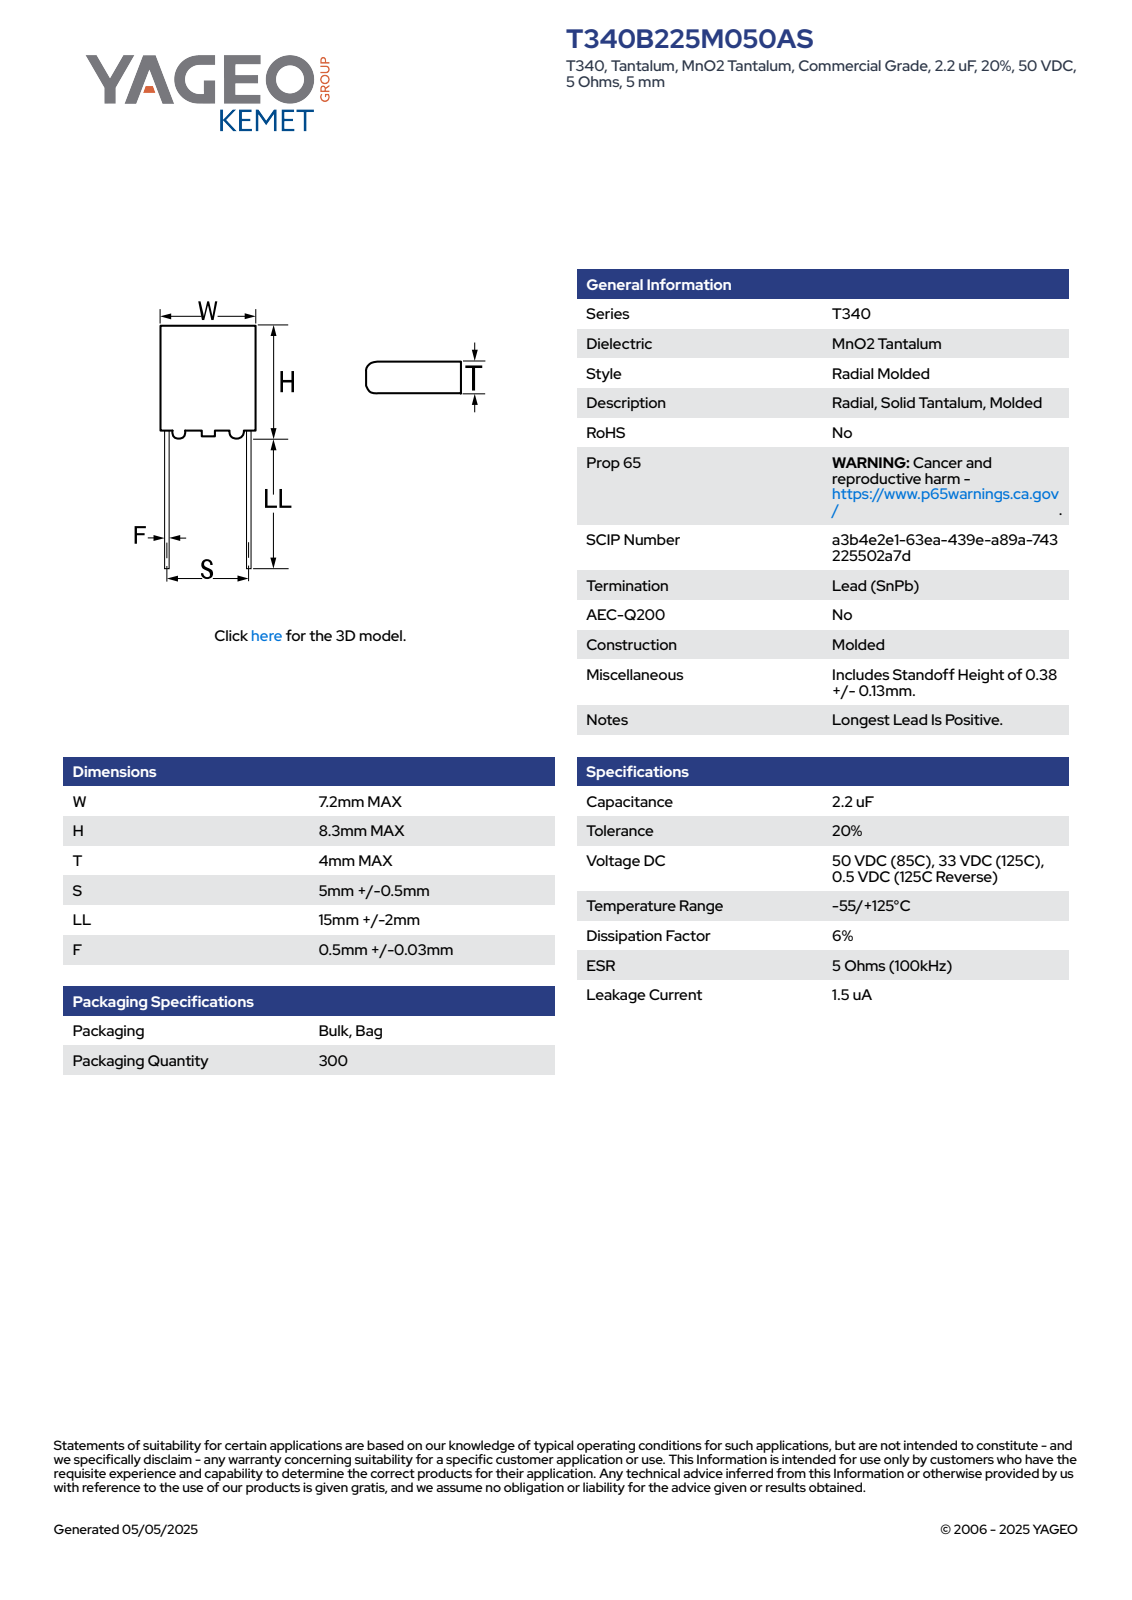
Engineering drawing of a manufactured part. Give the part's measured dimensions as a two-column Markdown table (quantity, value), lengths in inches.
| quantity | value |
| --- | --- |
| part name | CTR_T340B_W7.2H8.3T4S5LL17F0.53G0.51 |
| STEP written by | SolidWorks 2014 (AUTOMOTIVE_DESIGN) |
| units | inches |
| bodies | 4 solids, 79 faces (71 planar, 8 cylindrical, 0 other) |
| overall size | 1.016 × 0.283 × 0.157 |
| volume | 0.015 in³ |
| surface area | 0.482 in² |
| round bosses / shafts (diameter × count) | 0.021 × 2 |
| partial cylindrical surfaces (radius × count) | 0.02 × 2, 0.039 × 2 |
| main face-to-face distances | 0.157, 0.283, 0.327, 0.02, 0.347, 0.116, 0.167, 0.158, 0.051, 0.669 |
